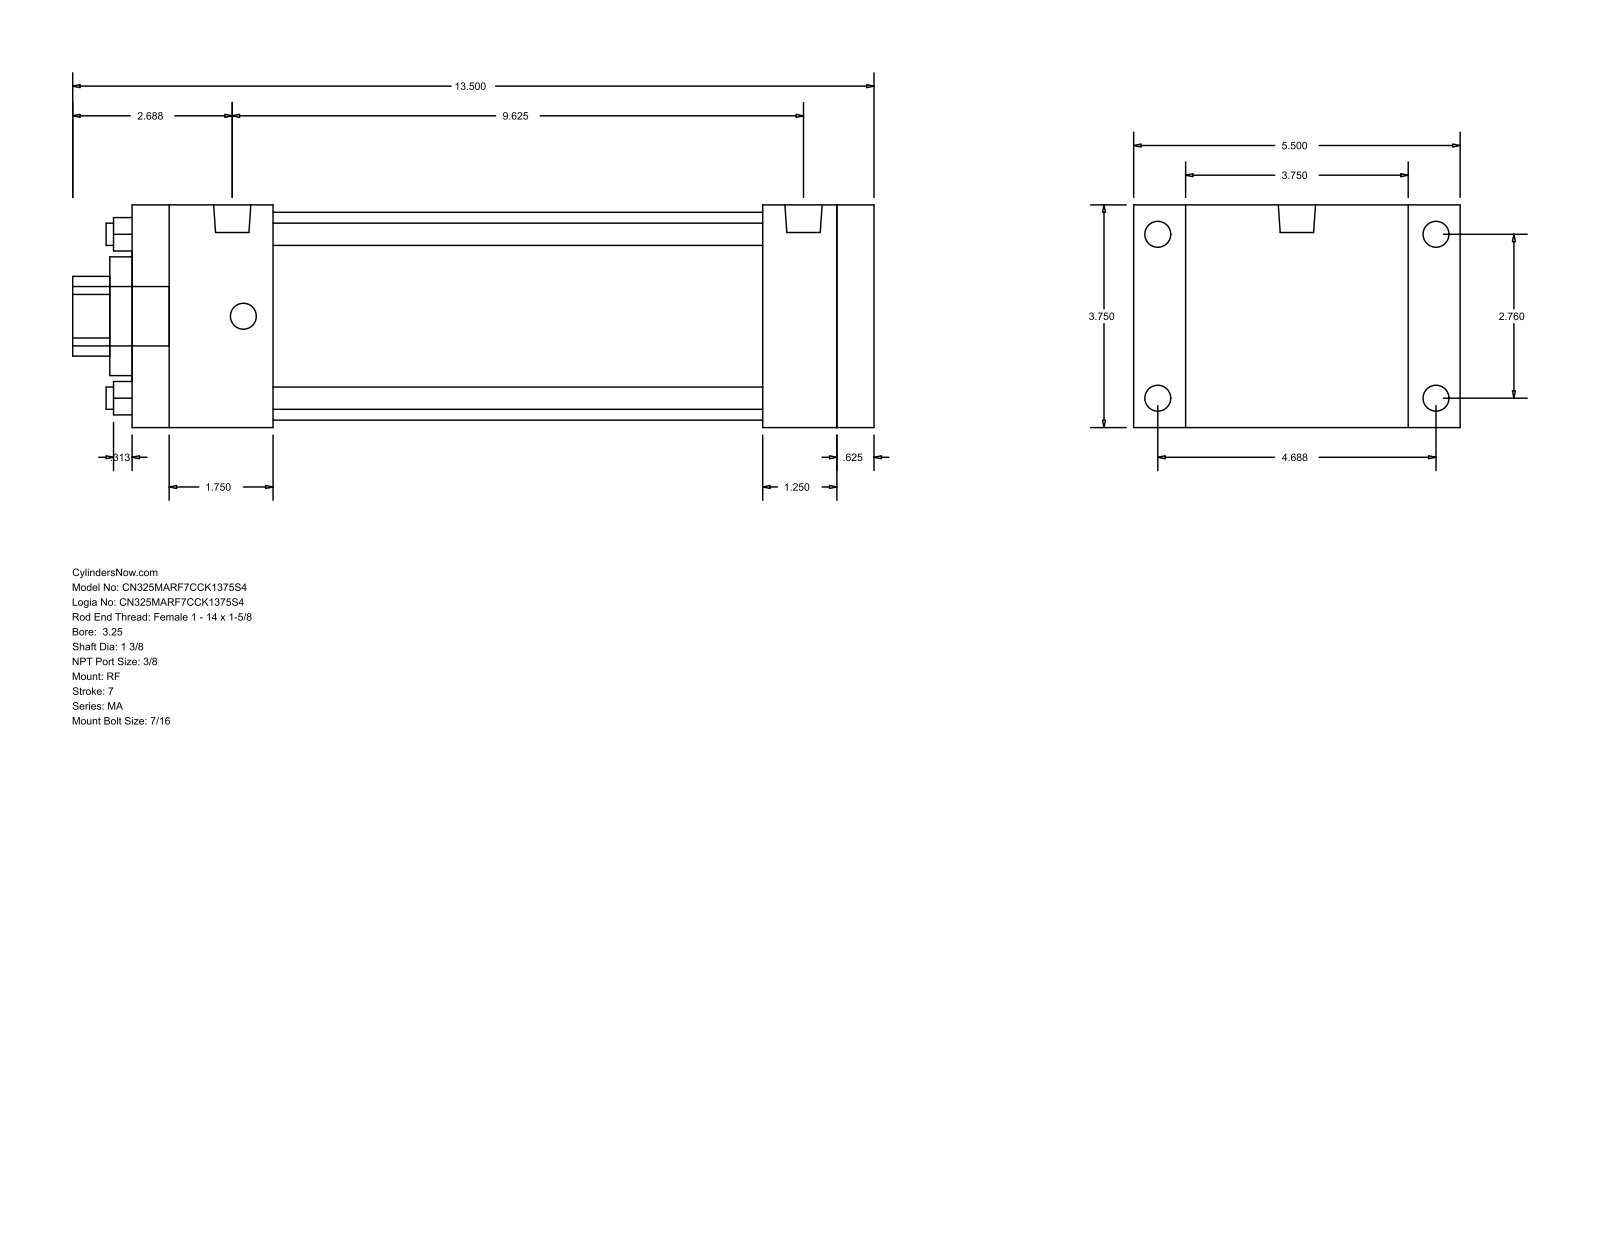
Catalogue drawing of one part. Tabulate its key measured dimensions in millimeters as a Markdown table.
| quantity | value |
| --- | --- |
| part name | MA_RF__0325_1.375 |
| STEP written by | GSSL Pune (CONFIG_CONTROL_DESIGN) |
| units | millimeters |
| bodies | 0 solids, 92 faces (64 planar, 28 cylindrical, 0 other) |
| overall size | 342.9 × 139.7 × 95.25 |
| round holes (diameter × count) | 9.53 × 4, 34.92 × 1, 50.8 × 1, 88.9 × 1 |
| round bosses / shafts (diameter × count) | 11.11 × 8, 15.93 × 2, 25.4 × 1 |
| partial cylindrical surfaces (radius × count) | 17.06 × 1 |
| main face-to-face distances | 95.24, 317.5, 15.88, 301.62, 22.23, 117.47, 269.87, 31.75, 47.63, 60.32 |
| hole center spacings | 49.57, 70.1, 99.14 |
